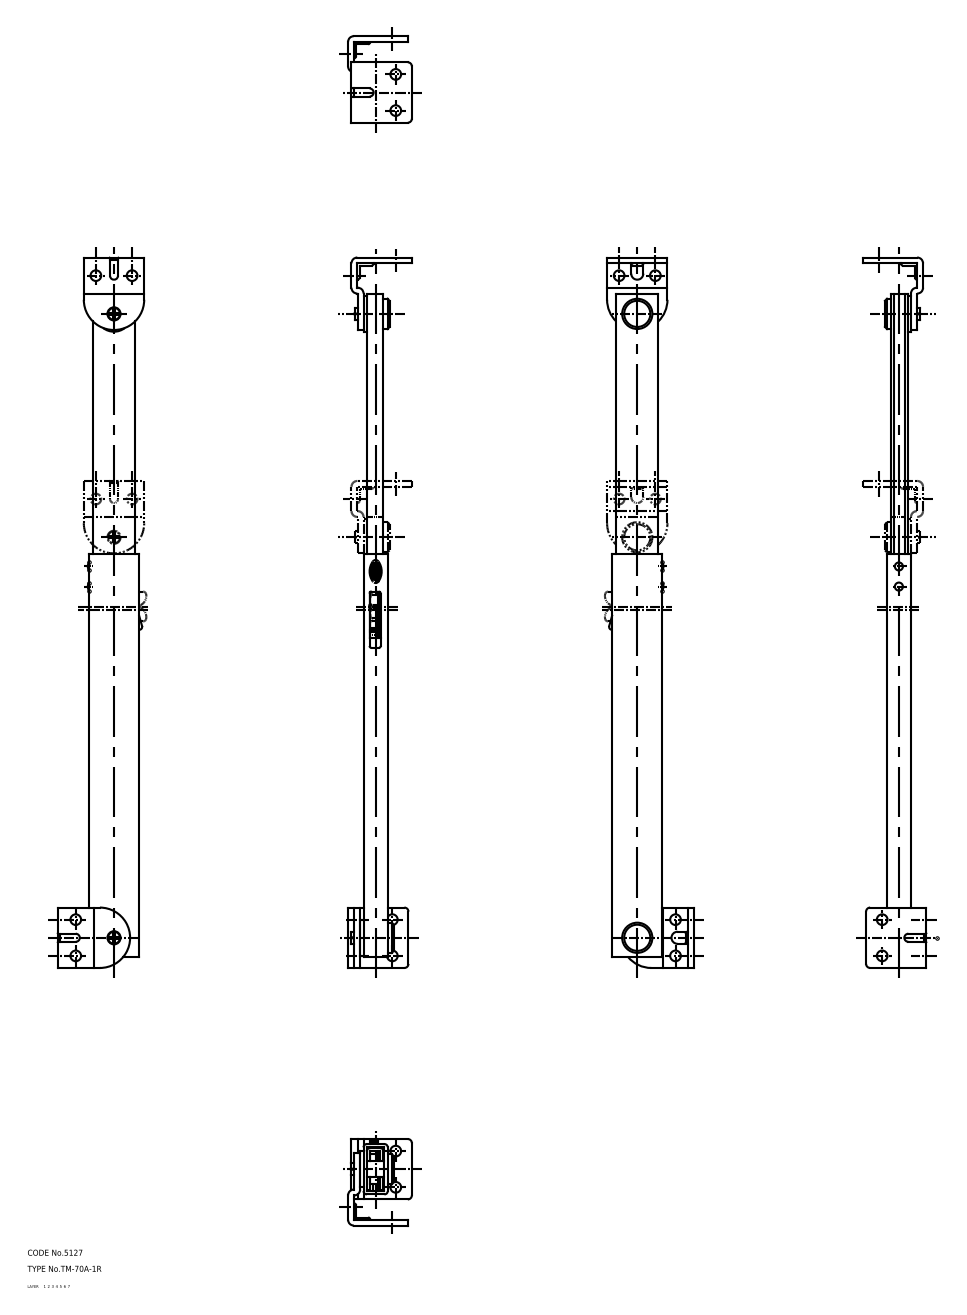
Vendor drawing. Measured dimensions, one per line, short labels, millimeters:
name: rivet_3; rivet_2; rivet_1; bracket_A (+7 more)
written by: CADfix (AUTOMOTIVE_DESIGN)
unit: mm
bodies: 12 solids, 282 faces (0 planar, 0 cylindrical, 282 other)
size: 353 × 43 × 31.7
volume: 50 221 mm³; area: 58 444 mm²
